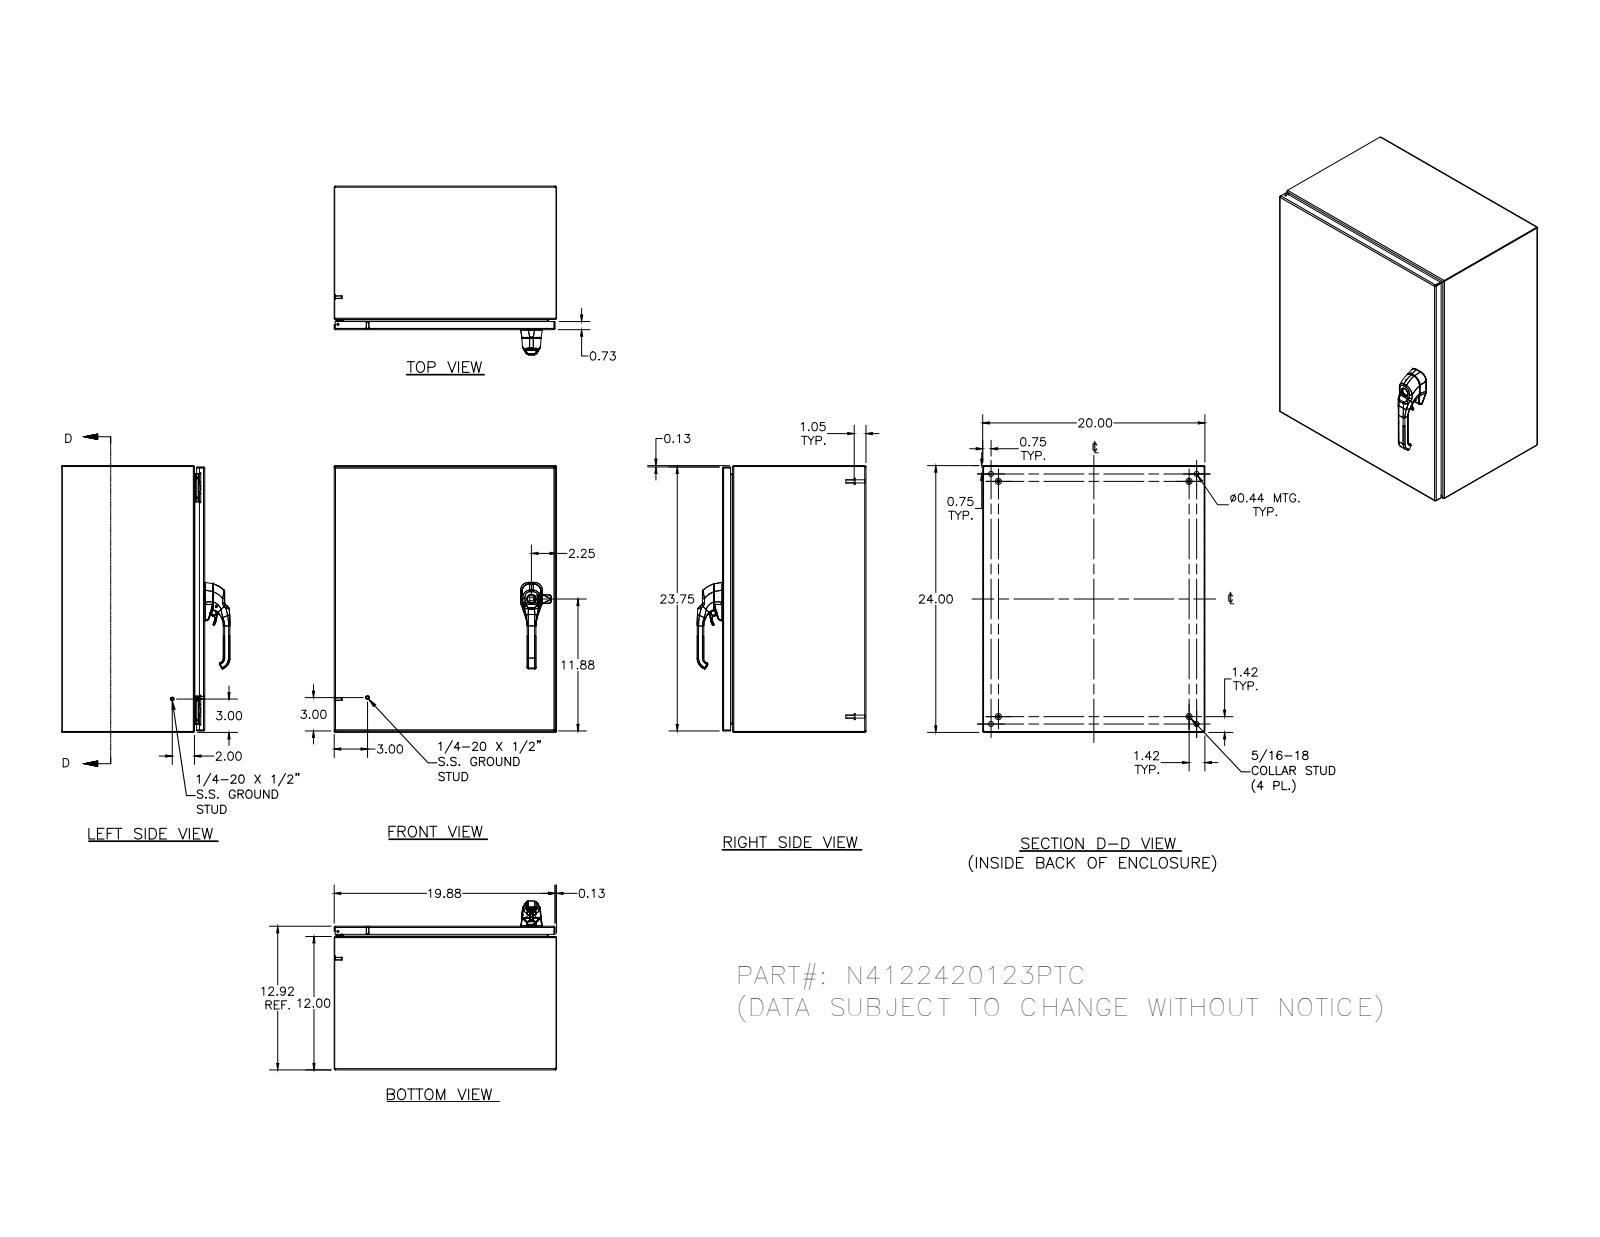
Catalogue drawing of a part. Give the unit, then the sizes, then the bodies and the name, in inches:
Units: inches
Overall size (bounding box): 24 × 20 × 15.095
Round holes (diameter × count): ⌀0.188 ×5, ⌀0.093 ×4, ⌀0.152 ×4, ⌀0.167 ×4, ⌀0.172 ×4, ⌀0.437 ×4, ⌀0.156 ×2, ⌀0.187 ×1, ⌀0.413 ×1
Round bosses / shafts (diameter × count): ⌀0.25 ×10, ⌀0.563 ×4, ⌀0.36 ×4, ⌀0.32 ×4, ⌀0.3 ×4, ⌀0.275 ×4, ⌀0.256 ×4, ⌀0.164 ×4
Partial cylindrical surfaces — rounded edges, fillets, slot ends (radius × count): R0.031 ×30, R0.05 ×26, R0.105 ×20, R0.016 ×18, R0.125 ×14, R0.02 ×11, R0.032 ×8, R0.067 ×8
Main face-to-face distances: 0.074, 12.843, 19.926, 23.926, 12.917, 12.769, 19.852, 20, 24, 23.852
Hole centre spacings: 19.996, 18.872, 0.017, 0.66, 20.656, 0.019, 0.5, 0.648
Volume: 171.7 in³ · Surface area: 4 440 in²
Bodies: 29 solids, 1333 faces (433 planar, 495 cylindrical, 405 other)
Part name (STEP PRODUCT): N4122420123PTC
STEP written by: SolidWorks 2018 (AUTOMOTIVE_DESIGN)
